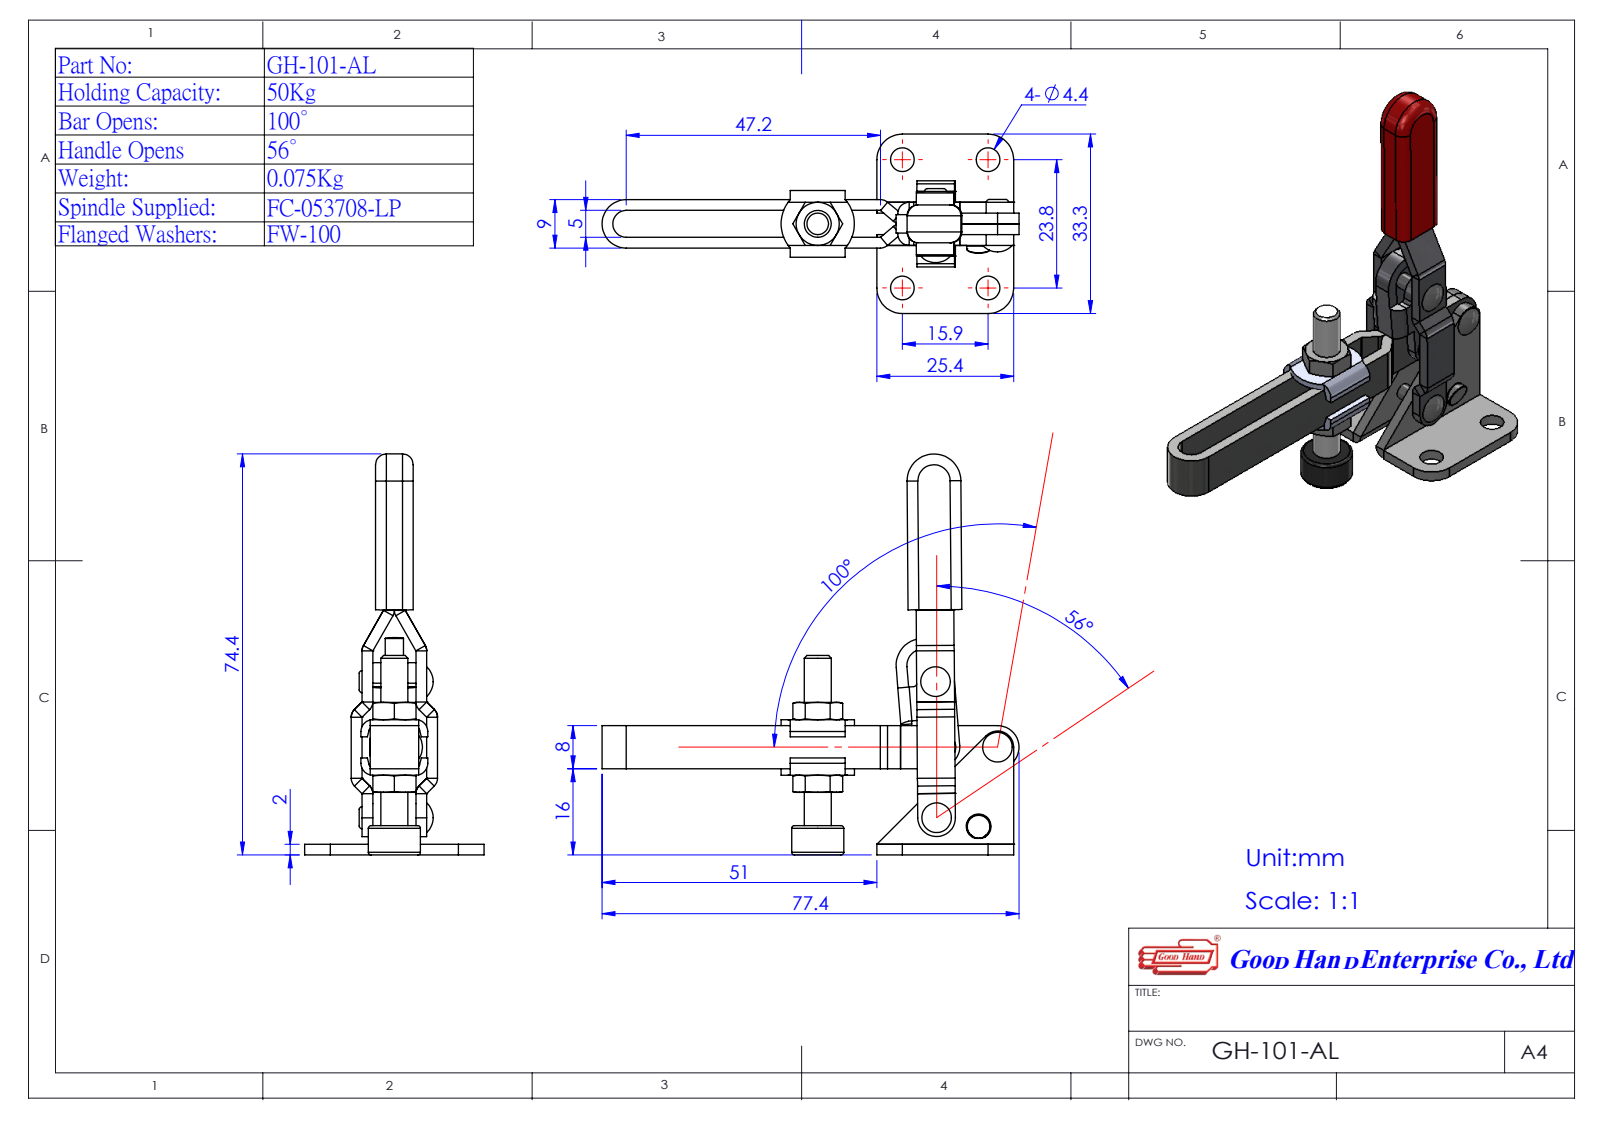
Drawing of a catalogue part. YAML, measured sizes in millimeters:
part_name: "1101AL09_GH-101-A; Group1^493778(GH-101-A); Group2^493778(GH-101-A); Group5^493778(GH-101-A) (+2 more)"
step_written_by: "SolidWorks 2016 (AUTOMOTIVE_DESIGN)"
units: millimeters
bodies: {solids: 5, faces: 303, planar: 129, cylindrical: 115, other: 59}
overall_size: [77.4, 74.4, 33.3]
volume: 10587
surface_area: 11559
round_holes:
  - {diameter: 2.5, count: 4}
  - {diameter: 4.4, count: 4}
  - {diameter: 3.05, count: 1}
round_bosses_or_shafts:
  - {diameter: 9.65, count: 1}
  - {diameter: 5, count: 1}
  - {diameter: 3, count: 1}
partial_cylinders:
  - {radius: 1, count: 6}
  - {radius: 0.1, count: 5}
  - {radius: 2.2, count: 5}
  - {radius: 2.1, count: 4}
  - {radius: 4.75, count: 4}
  - {radius: 3.5, count: 3}
  - {radius: 2.01, count: 2}
  - {radius: 2.09, count: 2}
face_to_face_distances: [2, 0.5, 1.5, 6, 8, 6.5, 8.5, 7, 4, 1]
hole_center_spacings: [15.9, 23.8, 28.62, 10.5, 12.2, 13.11, 16.74, 17.29]
